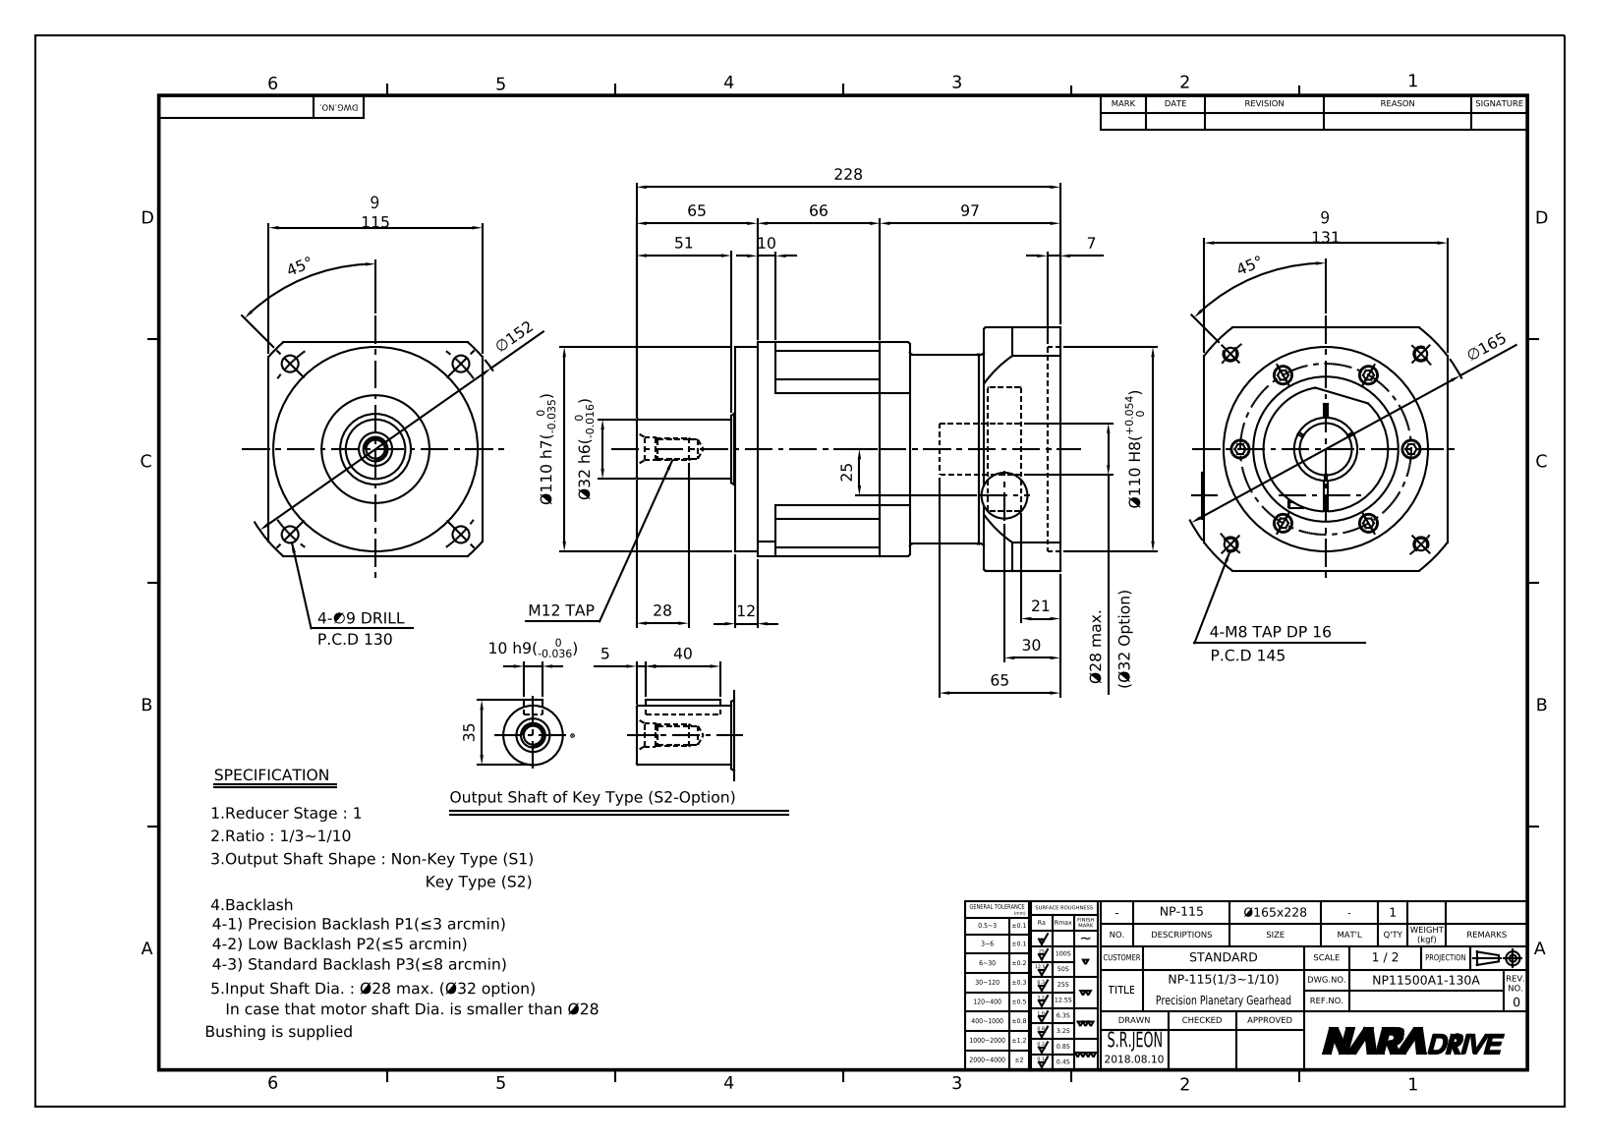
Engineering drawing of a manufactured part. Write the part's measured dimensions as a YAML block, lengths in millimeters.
part_name: "NP11500A1-130A-S1"
step_written_by: "Autodesk Inventor 2015 (AUTOMOTIVE_DESIGN)"
units: millimeters
bodies: {solids: 2, faces: 436, planar: 200, cylindrical: 127, other: 109}
overall_size: [228, 132, 131]
volume: 1578000
surface_area: 199169
round_holes:
  - {diameter: 4.92, count: 10}
  - {diameter: 6.6, count: 10}
  - {diameter: 11, count: 10}
  - {diameter: 6.65, count: 5}
  - {diameter: 9, count: 5}
  - {diameter: 10.11, count: 1}
  - {diameter: 10.25, count: 1}
  - {diameter: 12.5, count: 1}
  - {diameter: 14.5, count: 1}
  - {diameter: 28, count: 1}
  - {diameter: 34, count: 1}
  - {diameter: 58, count: 1}
round_bosses_or_shafts:
  - {diameter: 10, count: 10}
  - {diameter: 6, count: 10}
  - {diameter: 102, count: 1}
  - {diameter: 67, count: 1}
  - {diameter: 38, count: 1}
  - {diameter: 32, count: 1}
  - {diameter: 25, count: 1}
  - {diameter: 14, count: 1}
partial_cylinders:
  - {radius: 1, count: 12}
  - {radius: 0.5, count: 4}
  - {radius: 12.5, count: 4}
  - {radius: 7, count: 1}
  - {radius: 65, count: 1}
  - {radius: 76, count: 1}
  - {radius: 82.5, count: 1}
face_to_face_distances: [8, 123, 68, 115, 66, 56, 10, 131, 2, 41]
hole_center_spacings: [46, 97.37, 7.5, 17.38, 22.06, 45.99, 75.32, 79.67]
